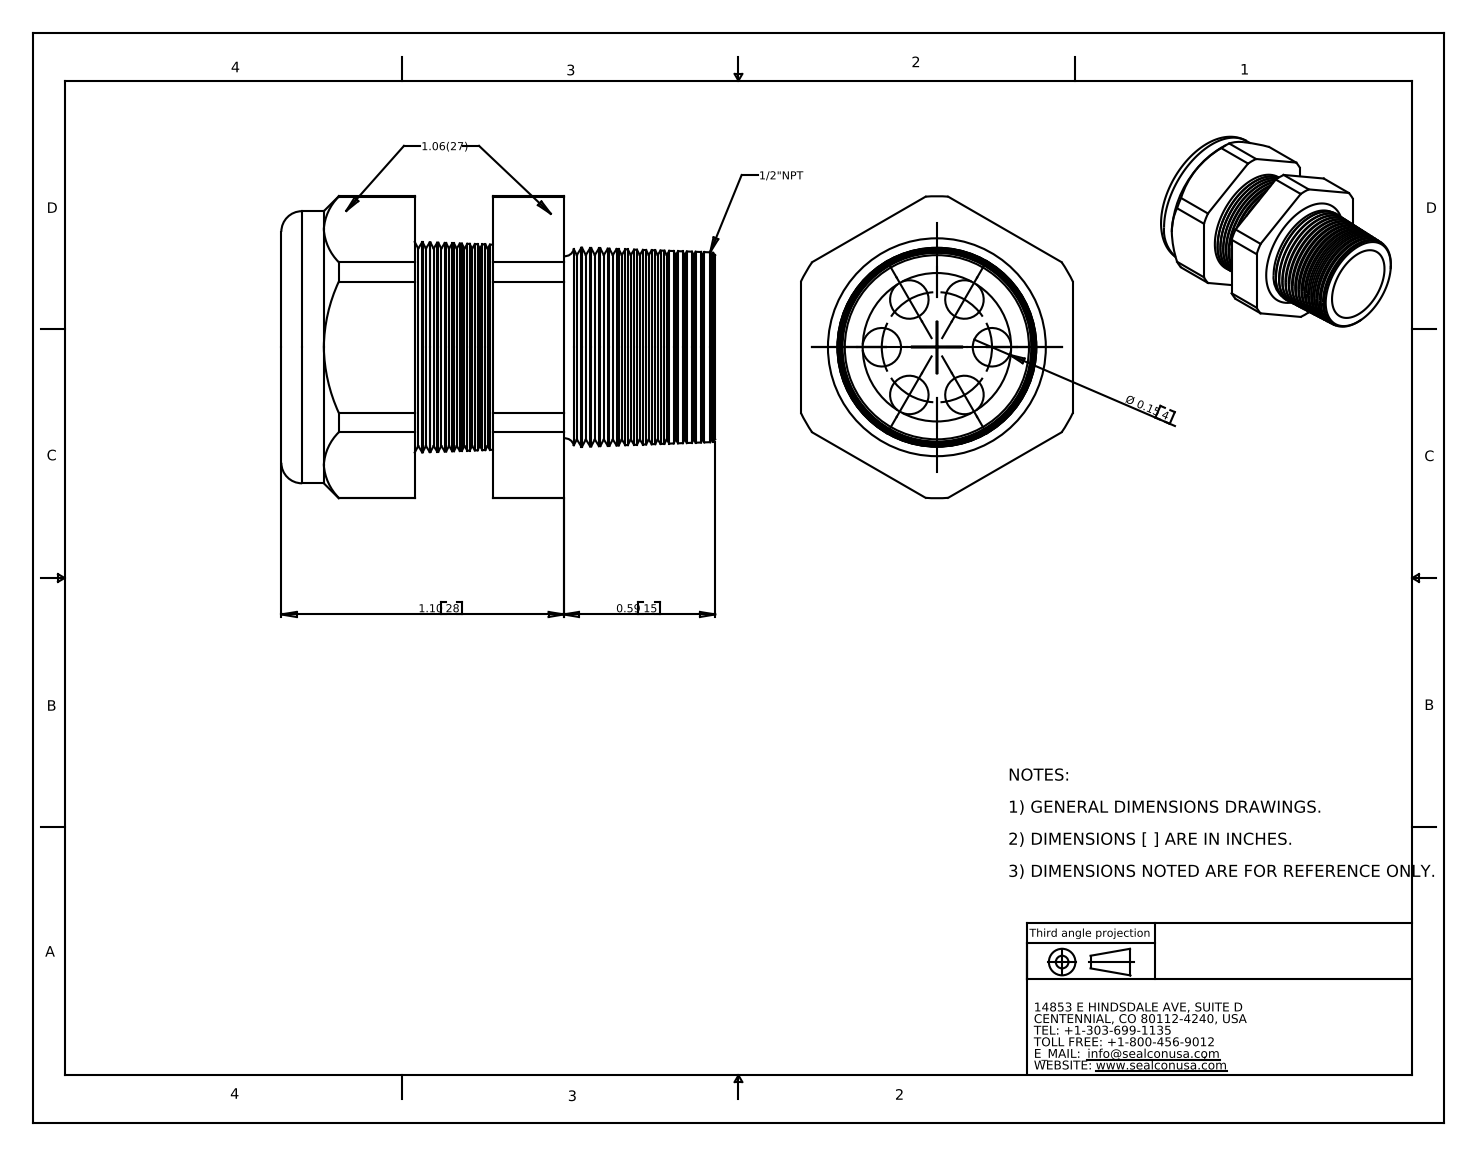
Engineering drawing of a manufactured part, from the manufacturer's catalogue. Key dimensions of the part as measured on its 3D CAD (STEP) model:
Part name (STEP PRODUCT): CD16N0-BK
STEP written by: SolidWorks 2007 (CONFIG_CONTROL_DESIGN)
Units: inches
Bodies: 2 solids, 222 faces (20 planar, 32 cylindrical, 170 other)
Overall size (bounding box): 1.69 × 1.177 × 1.06
Volume: 0.744 in³ · Surface area: 13.73 in²
Round holes (diameter × count): ⌀0.15 ×6, ⌀0.58 ×1, ⌀0.6 ×1
Round bosses / shafts (diameter × count): ⌀1.06 ×1
Partial cylindrical surfaces — rounded edges, fillets, slot ends (radius × count): R0.588 ×1
Main face-to-face distances: 1.06, 0.305, 0.58, 0.276, 0.52, 0.824, 1.1, 0.35, 0.17, 0.474
Hole centre spacings: 0.215, 0.372, 0.215, 0.43, 0.429
